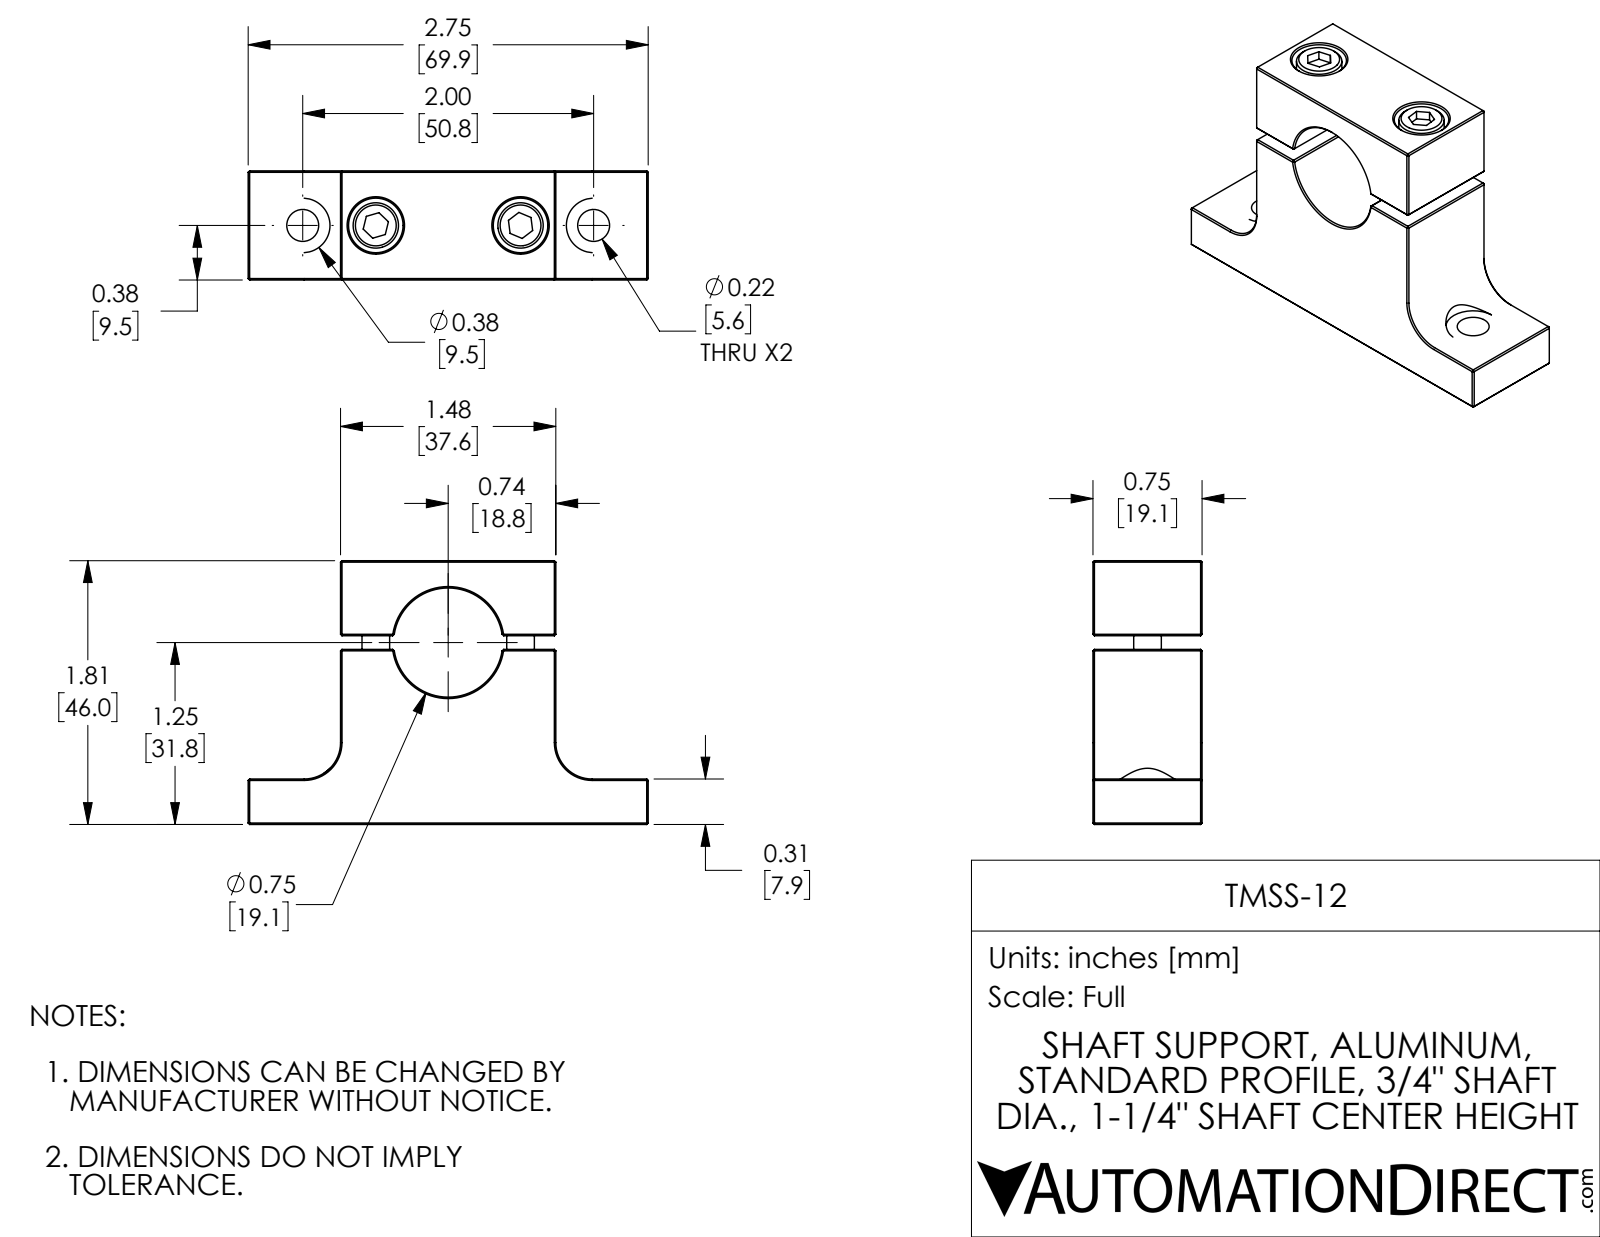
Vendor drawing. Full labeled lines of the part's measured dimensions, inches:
Part name (STEP PRODUCT): TMSS-12
STEP written by: SolidWorks 2017 (AUTOMOTIVE_DESIGN)
Units: inches
Bodies: 4 solids, 165 faces (110 planar, 31 cylindrical, 24 other)
Overall size (bounding box): 2.75 × 1.813 × 0.75
Volume: 1.885 in³ · Surface area: 17.91 in²
Round holes (diameter × count): ⌀0.145 ×2, ⌀0.201 ×2, ⌀0.22 ×2, ⌀0.375 ×2, ⌀0.75 ×1
Round bosses / shafts (diameter × count): ⌀0.312 ×2, ⌀0.19 ×2
Partial cylindrical surfaces — rounded edges, fillets, slot ends (radius × count): R0.187 ×2, R0.25 ×2
Main face-to-face distances: 0.75, 1.813, 1.48, 0.313, 1.5, 1.203, 0.891, 0.609, 1.297, 0.984
Hole centre spacings: 0.502, 1.498, 0.995, 2
